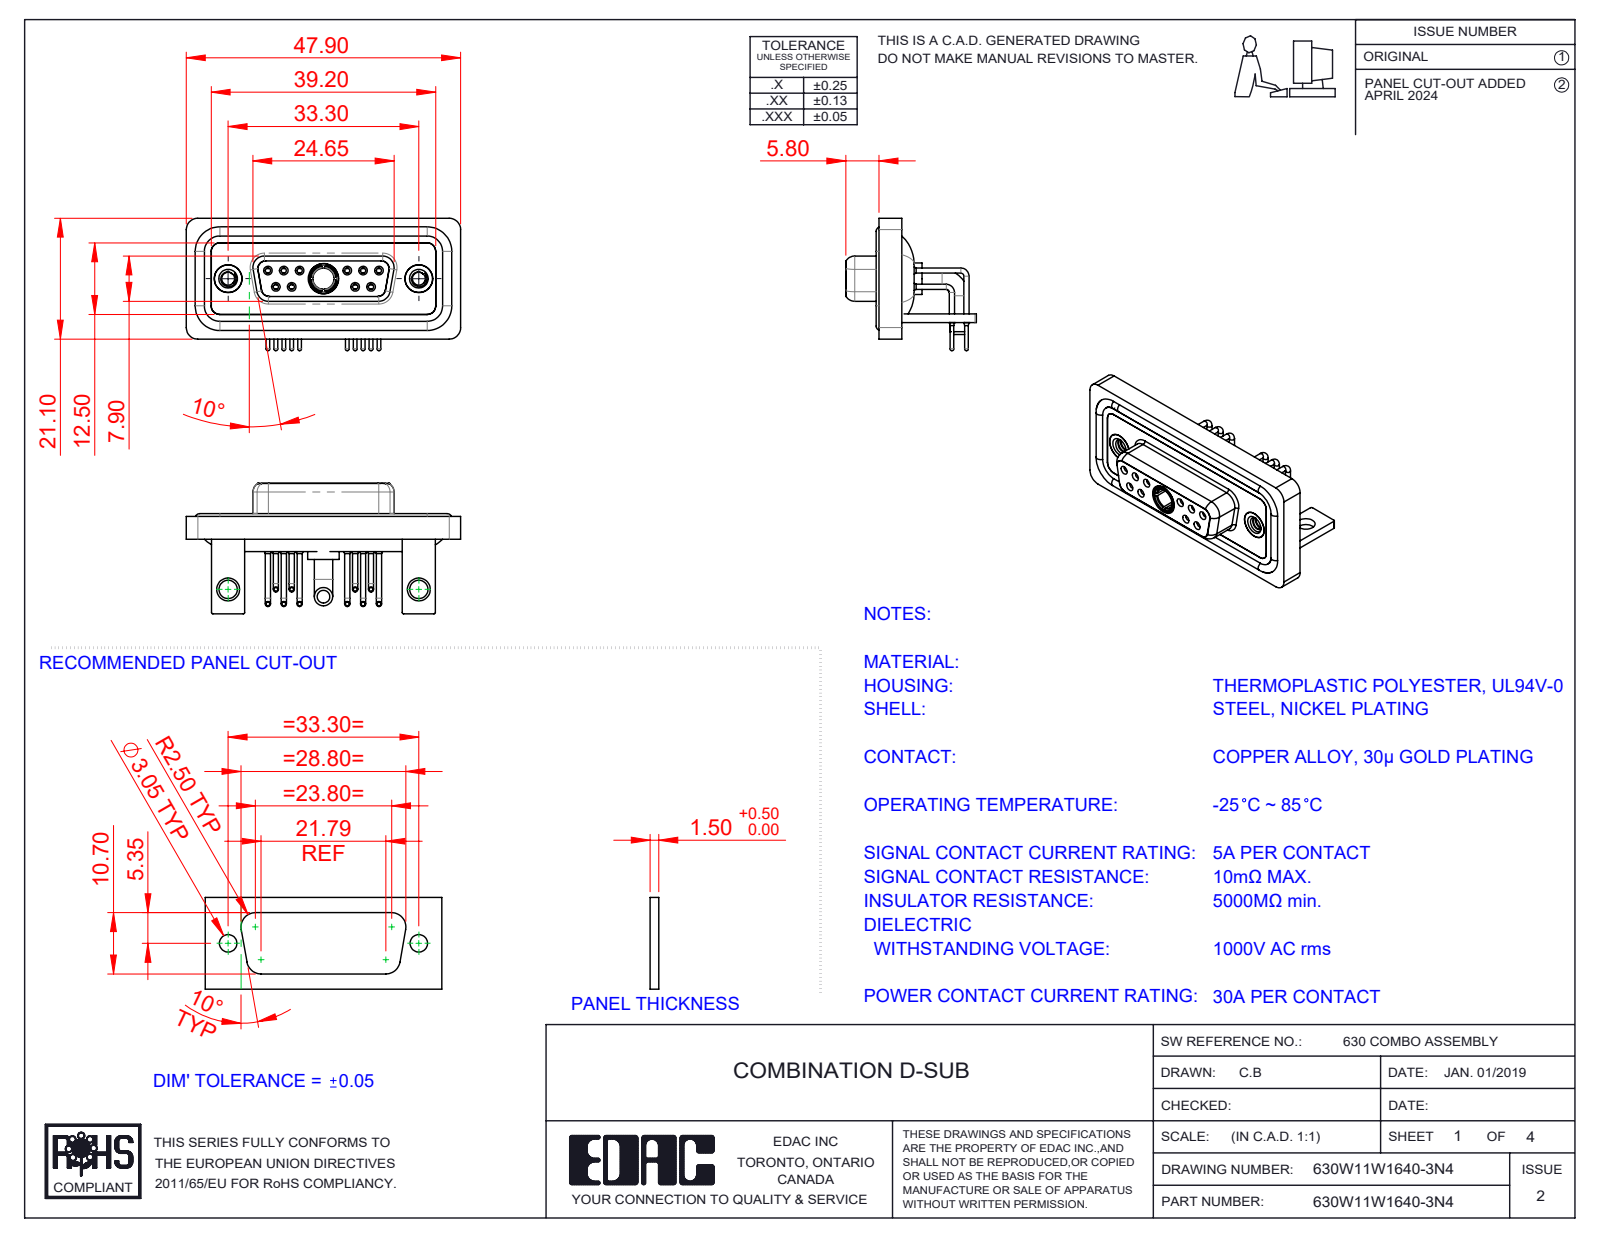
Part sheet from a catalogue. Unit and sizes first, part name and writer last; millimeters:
Units: millimetres
Overall size (bounding box): 47.9 × 23.12 × 22.8
Round holes (diameter × count): ⌀0.9 ×10, ⌀1.1 ×10, ⌀1.5 ×10, ⌀2 ×10, ⌀1.7 ×6, ⌀1.6 ×4, ⌀4.85 ×3, ⌀2.26 ×2, ⌀3.2 ×2, ⌀4 ×2, ⌀4.05 ×2, ⌀5 ×2
Round bosses / shafts (diameter × count): ⌀1.6 ×10, ⌀0.9 ×10, ⌀0.65 ×10, ⌀4.95 ×2, ⌀4.8 ×2, ⌀3.2 ×2, ⌀5.5 ×1, ⌀5.2 ×1
Partial cylindrical surfaces — rounded edges, fillets, slot ends (radius × count): R2 ×21, R1.5 ×18, R0.25 ×16, R1.35 ×12, R1.6 ×8, R0.5 ×5, R0.6 ×4, R0.65 ×4
Main face-to-face distances: 0.4, 2.9, 1.8, 1.5, 3.7, 1.1, 1.6, 4.1, 0.8, 2.5
Hole centre spacings: 3.16, 2.77, 13.85, 11.08, 16.62, 5.03, 5.04, 5.54
Volume: 6 612 mm³ · Surface area: 11 225 mm²
Bodies: 21 solids, 1042 faces (304 planar, 467 cylindrical, 271 other)
Part name (STEP PRODUCT): 630Combo Threaded Rivet_2; 630Combo Shell Front_15 Contacts; 630Combo Waterproof Housing_15 Contacts; 630Combo Stabilizer Bracket_50 Contacts (+6 more)
STEP written by: SolidWorks 2023 (CONFIG_CONTROL_DESIGN)
